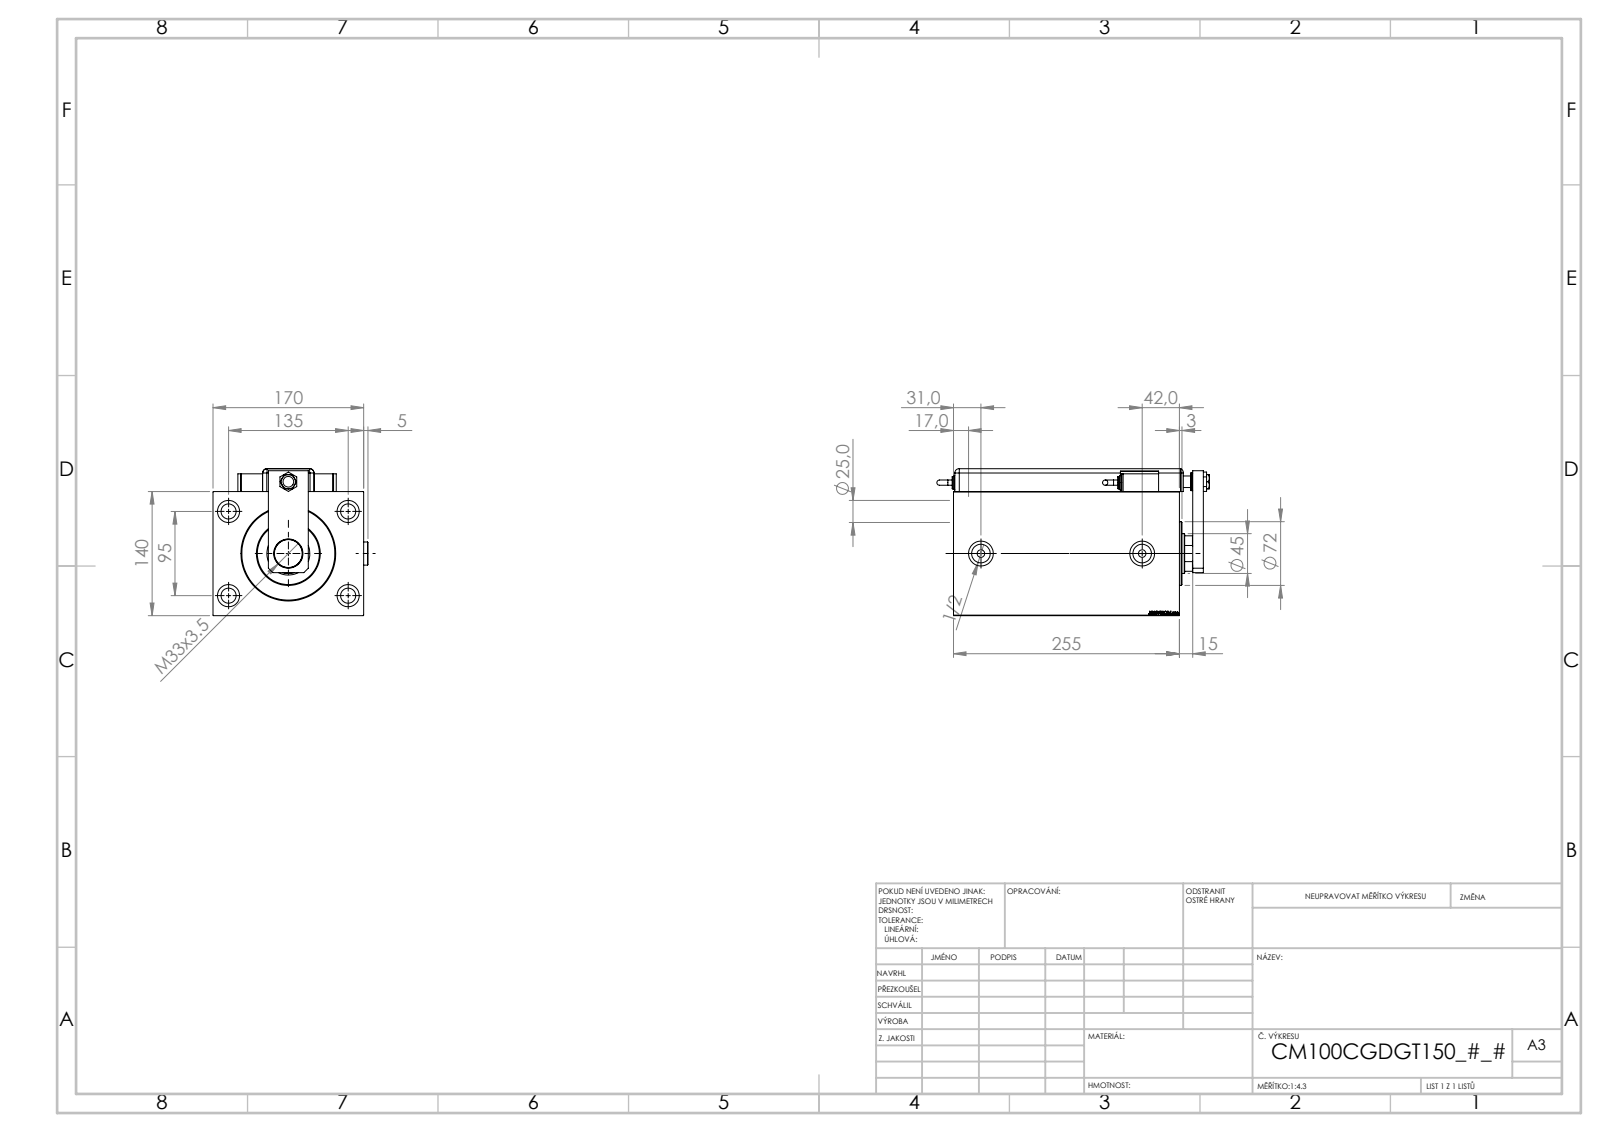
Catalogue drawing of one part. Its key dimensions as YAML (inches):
part_name: "MAGNETIC SWITCH Q; SWITCH_Q_FRONT_BACK; NUT_D19; NUT_D13 (+7 more)"
step_written_by: "SolidWorks 2019 (CONFIG_CONTROL_DESIGN)"
units: inches
bodies: {solids: 15, faces: 1303, planar: 649, cylindrical: 133, other: 521}
overall_size: [12.113, 6.886, 6.528]
volume: 310.6
surface_area: 821.2
round_holes:
  - {diameter: 0.669, count: 4}
  - {diameter: 0.984, count: 4}
  - {diameter: 0.157, count: 2}
  - {diameter: 0.315, count: 2}
  - {diameter: 0.335, count: 2}
  - {diameter: 0.825, count: 2}
  - {diameter: 1.102, count: 2}
  - {diameter: 0.472, count: 1}
  - {diameter: 0.512, count: 1}
  - {diameter: 0.551, count: 1}
  - {diameter: 1.24, count: 1}
  - {diameter: 1.299, count: 1}
round_bosses_or_shafts:
  - {diameter: 0.787, count: 3}
  - {diameter: 1.024, count: 2}
  - {diameter: 0.63, count: 2}
  - {diameter: 0.551, count: 2}
  - {diameter: 0.236, count: 2}
  - {diameter: 2.835, count: 1}
partial_cylinders:
  - {radius: 0.197, count: 9}
  - {radius: 0.394, count: 1}
  - {radius: 0.866, count: 1}
face_to_face_distances: [5.512, 6.693, 0.118, 10.039, 1.024, 9.016, 0.591, 1.016, 6.528, 6.409]
hole_center_spacings: [3.25, 2.967, 3.74, 5.315, 5.715, 6.499, 0.787, 3.189]
